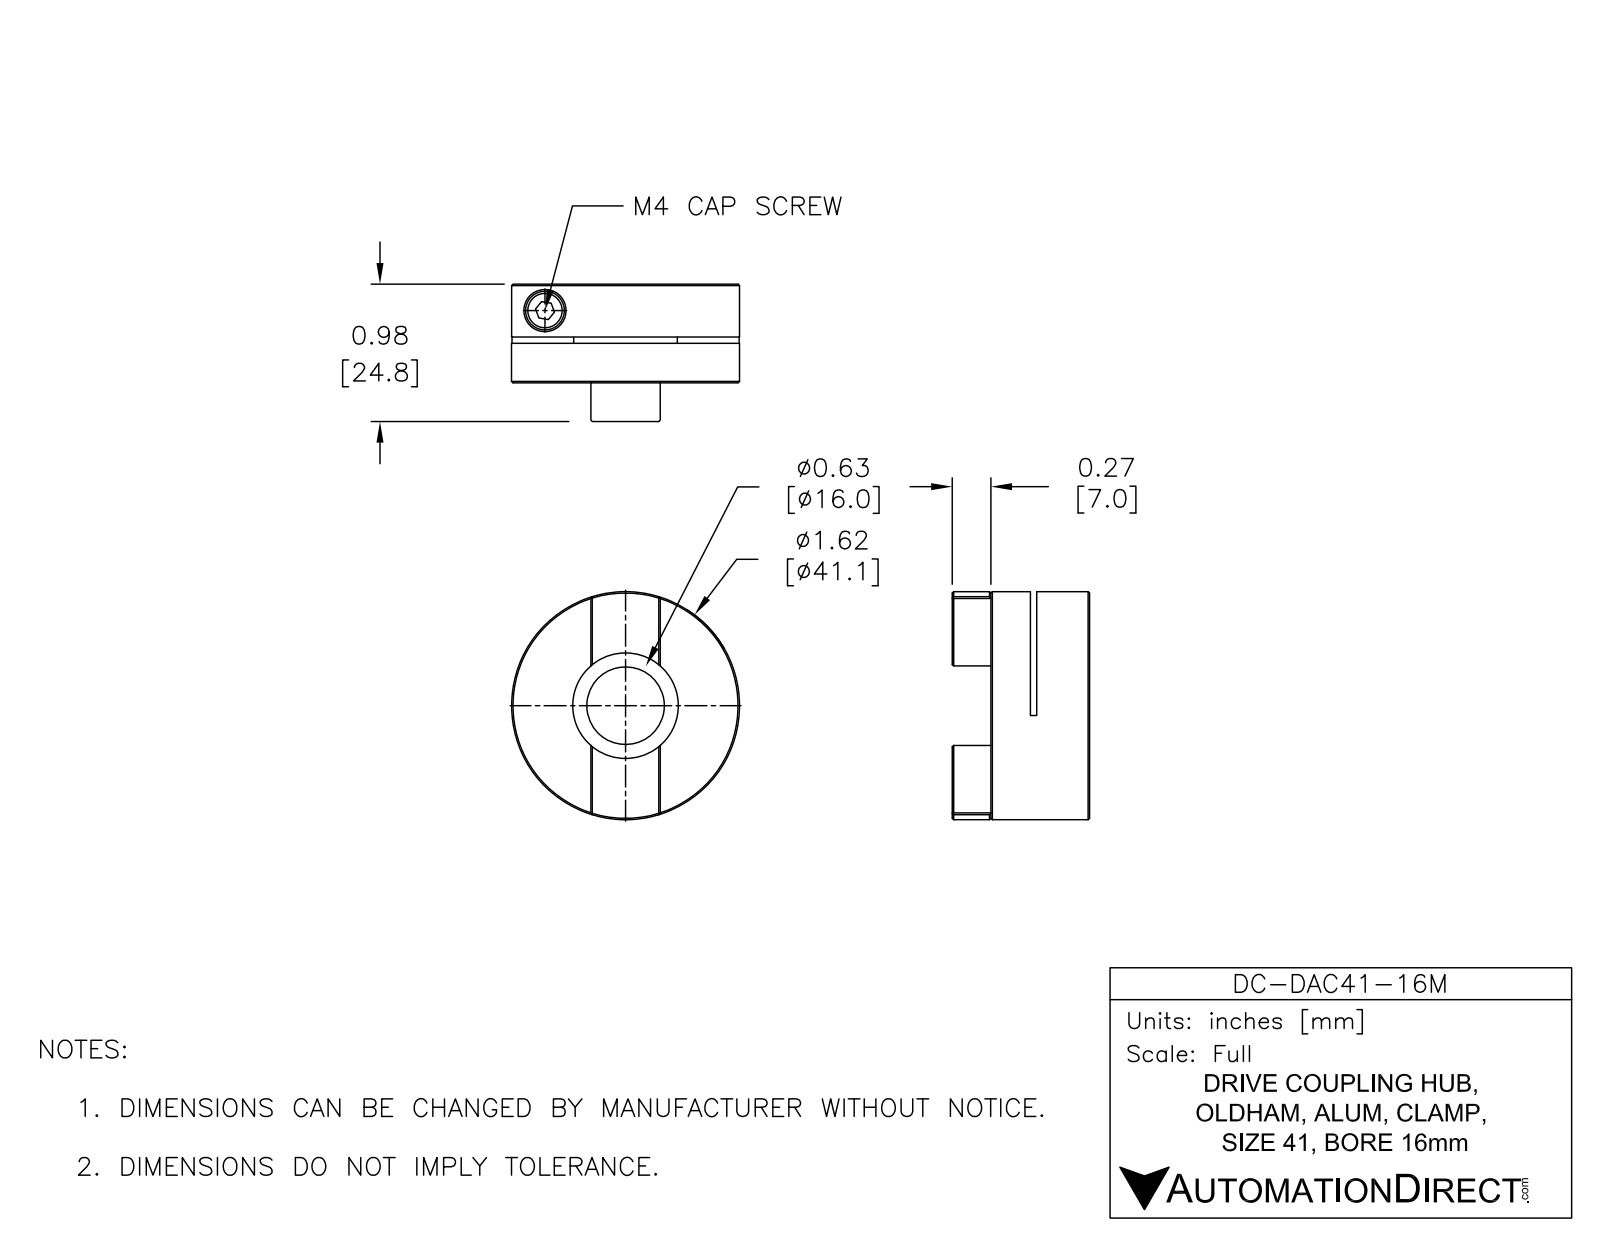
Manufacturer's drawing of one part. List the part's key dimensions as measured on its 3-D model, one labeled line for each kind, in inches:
Part name (STEP PRODUCT): DC-DAC41-16M
STEP written by: SolidWorks 2015 (AUTOMOTIVE_DESIGN)
Units: inches
Bodies: 1 solid, 52 faces (27 planar, 15 cylindrical, 10 other)
Overall size (bounding box): 1.62 × 1.62 × 0.976
Volume: 1.27 in³ · Surface area: 12.39 in²
Round holes (diameter × count): ⌀0.157 ×1, ⌀0.3 ×1, ⌀0.63 ×1
Round bosses / shafts (diameter × count): ⌀1.62 ×1
Partial cylindrical surfaces — rounded edges, fillets, slot ends (radius × count): R0.875 ×1
Main face-to-face distances: 0.701, 0.281, 0.42, 0.326, 0.045, 0.375, 0.274, 0.556, 0.6, 0.975
